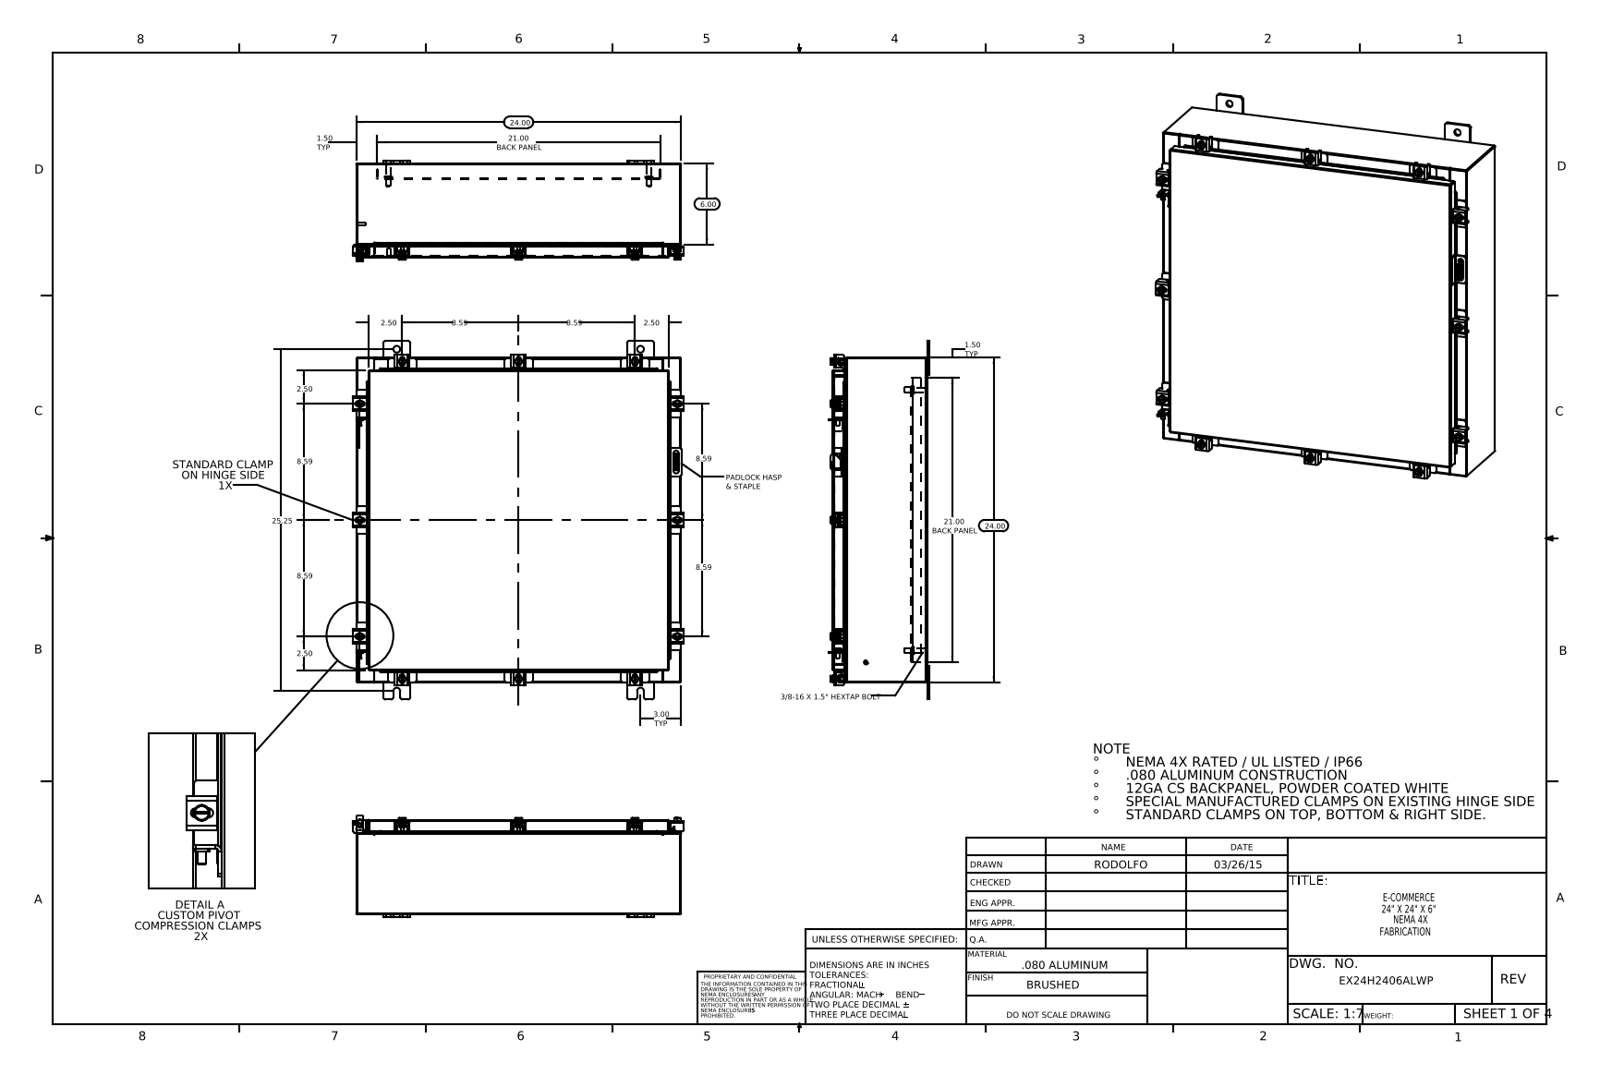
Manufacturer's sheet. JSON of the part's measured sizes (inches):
{"part_name": "22101002_RTP29; N-WMT04X30402202210-00 Clamp Top; EX24H2406ALWP Padlock Hasp; EX24H2406ALWP Padlock Staple (+8 more)", "step_written_by": "SolidWorks 2014 (CONFIG_CONTROL_DESIGN)", "units": "inches", "bodies": {"solids": 81, "faces": 2018, "planar": 1075, "cylindrical": 783, "other": 160}, "overall_size": [26.5, 24.421, 7.453], "volume_in3": 202.2, "surface_area_in2": 5023, "round_holes": [[0.213, 12], [0.26, 12], [0.5, 8], [0.125, 1], [0.25, 1]], "round_bosses_or_shafts": [[0.5, 12], [0.25, 12], [0.399, 10], [0.625, 4], [0.375, 4], [0.33, 4], [0.315, 2], [0.236, 2]], "partial_cylinders_radius": [[0.06, 54], [0.013, 24], [0.141, 24], [0.19, 24], [0.088, 22], [0.12, 22], [0.09, 18], [0.05, 17]], "face_to_face_distances": [0.075, 6.9, 23.925, 6.975, 6.826, 0.104, 1, 1.075, 5.826, 5.9], "hole_center_spacings": [8.594, 12.137, 20.559, 23.46, 24.976, 2.34, 18.34, 21.376]}
